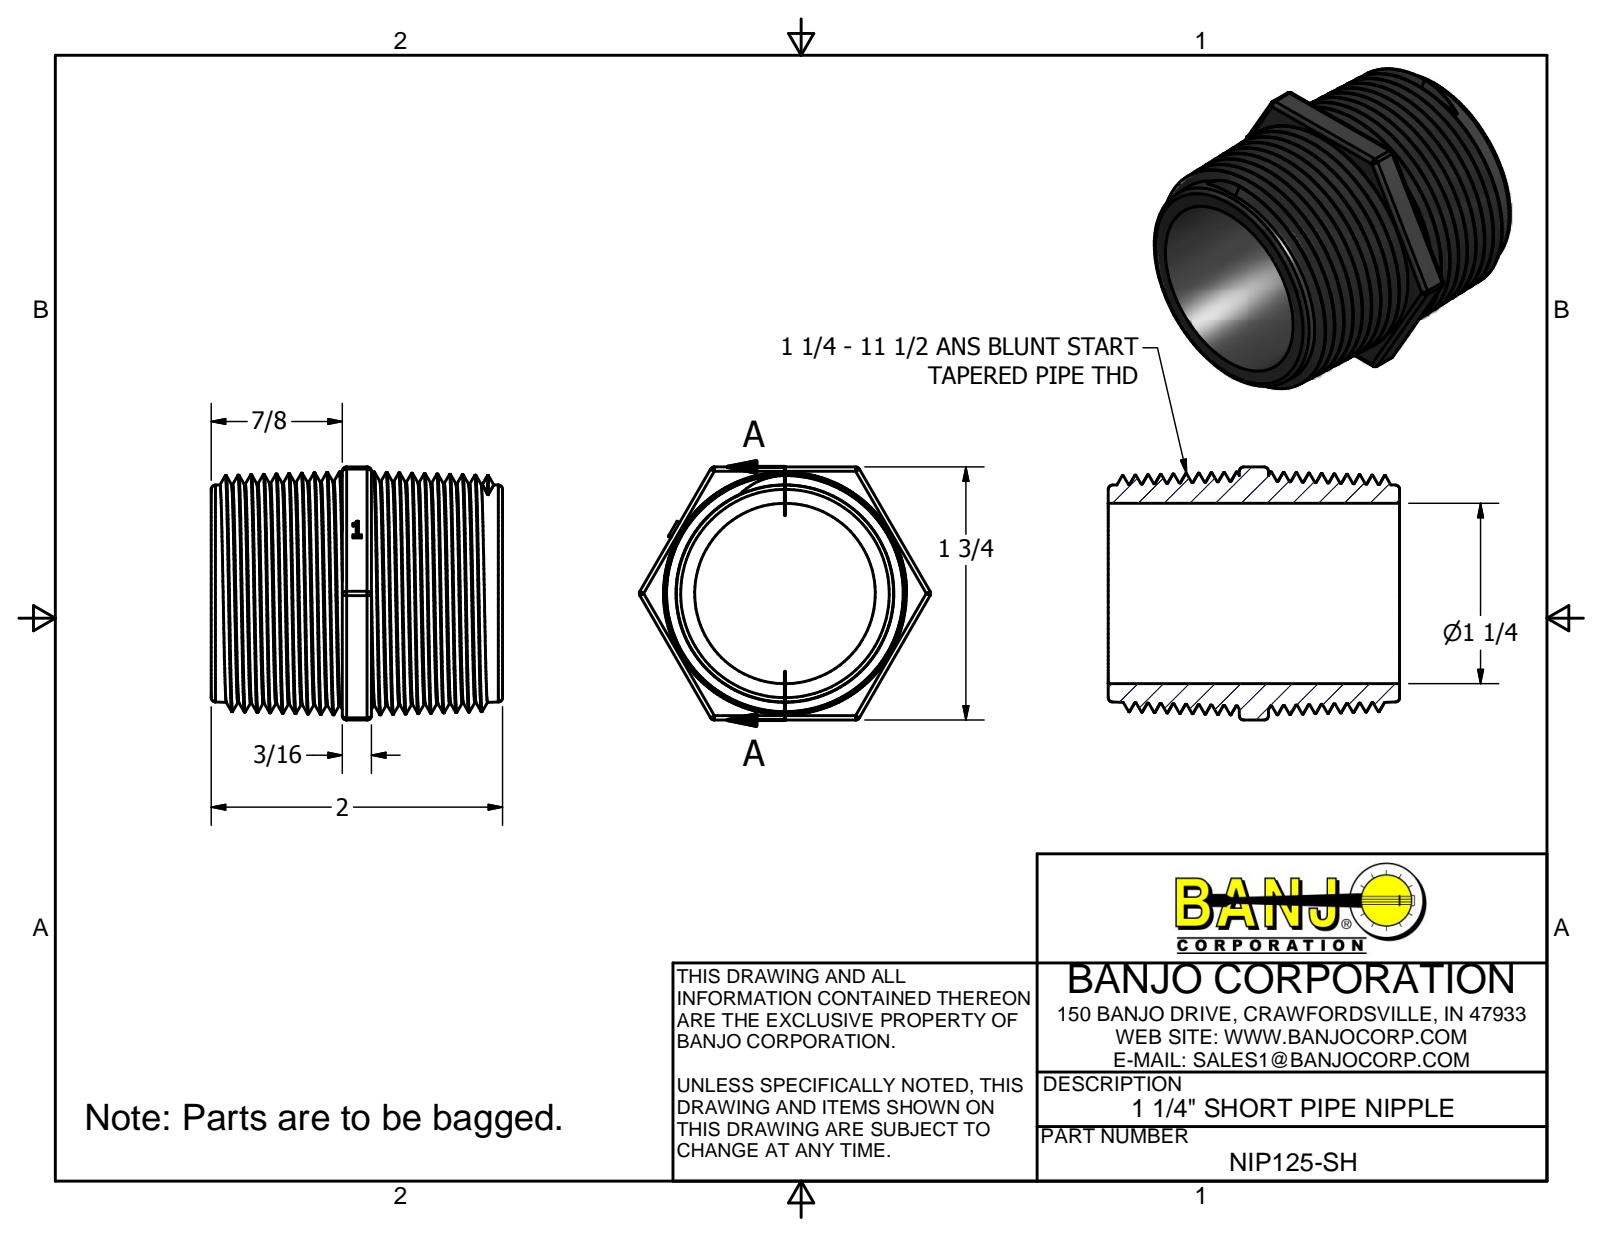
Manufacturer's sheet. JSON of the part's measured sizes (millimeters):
{"part_name": "NIP125-SH", "step_written_by": "Autodesk Inventor 2013 (AUTOMOTIVE_DESIGN)", "units": "millimeters", "bodies": {"solids": 1, "faces": 87, "planar": 23, "cylindrical": 19, "other": 45}, "overall_size": [50.8, 50.8, 44.2], "volume_mm3": 26280, "surface_area_mm2": 17120, "round_holes": [[31.5, 1]], "partial_cylinders_radius": [[0.8, 18]], "face_to_face_distances": [22.9, 27.9, 5.1, 44.2, 50.8, 44.7, 0.5, 25.7, 2.8, 2.3]}
